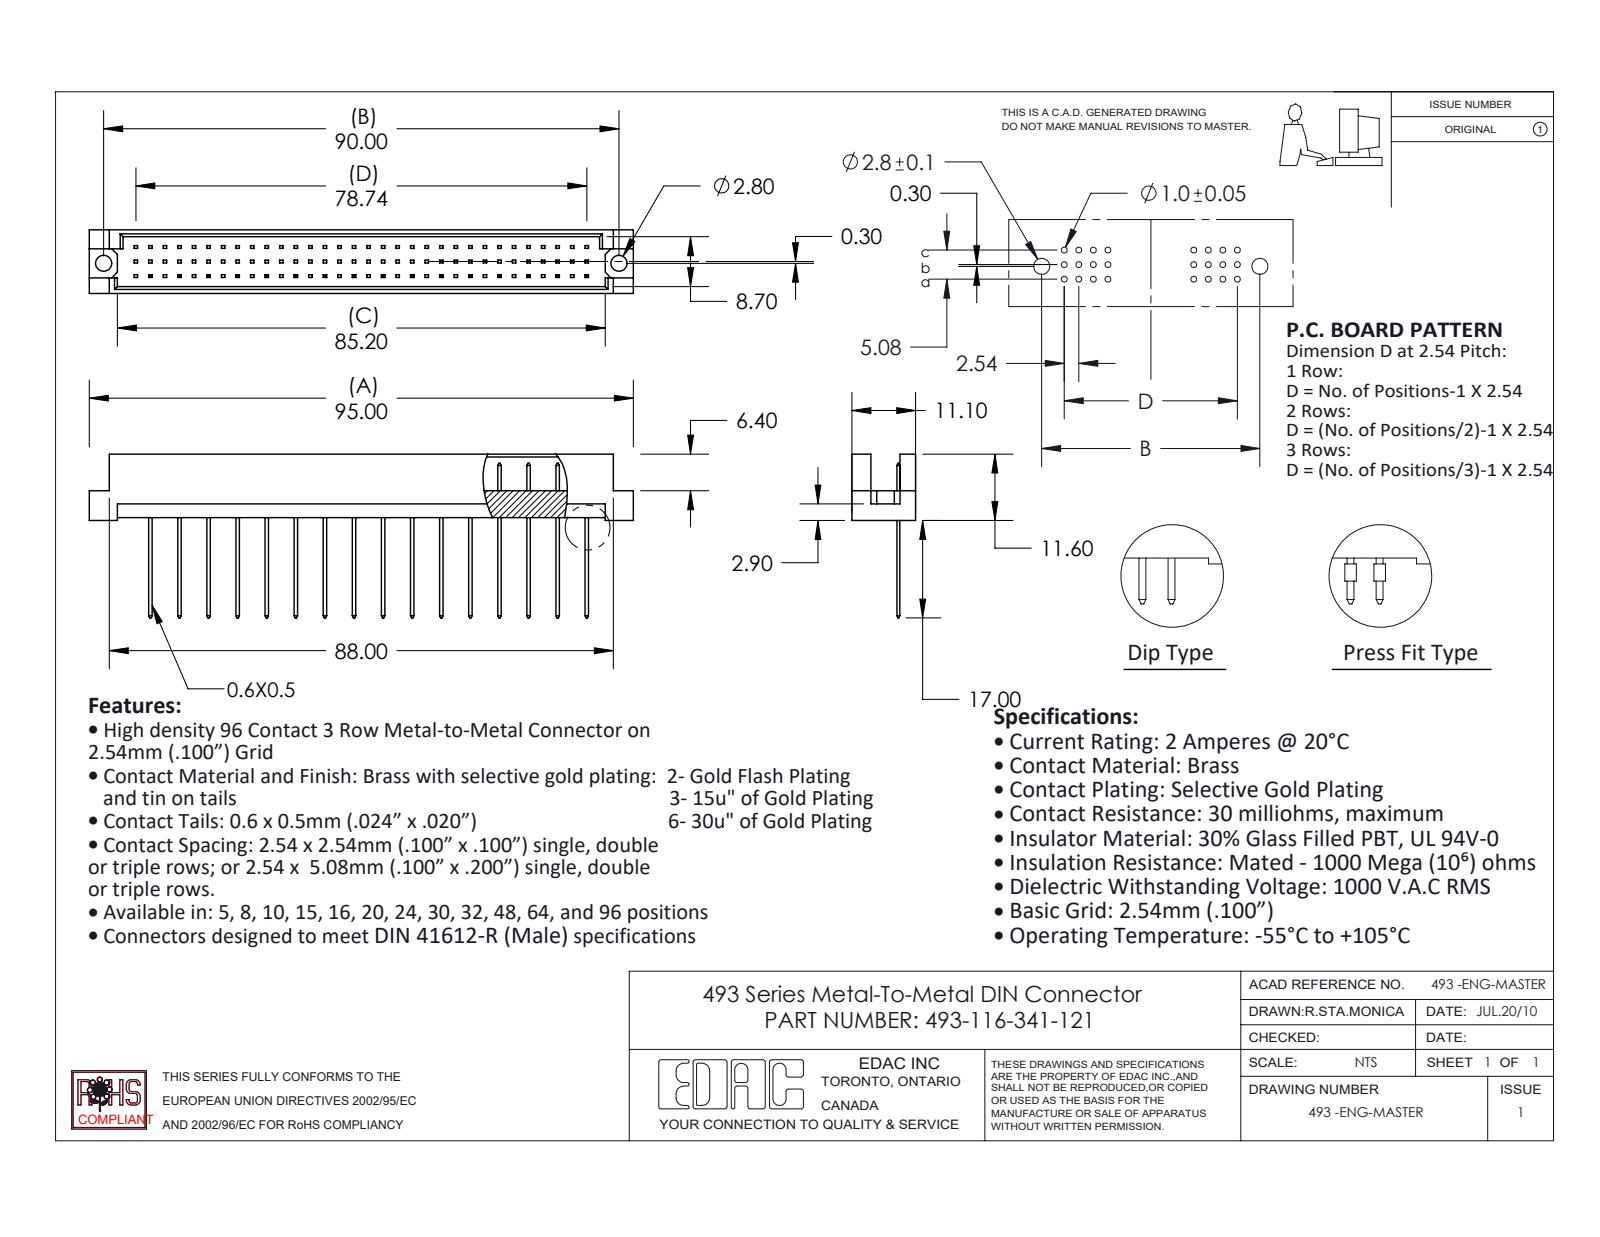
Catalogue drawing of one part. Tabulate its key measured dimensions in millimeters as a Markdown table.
| quantity | value |
| --- | --- |
| part name | 493 Part_96; 493-290_41; 493-116-341-121 |
| STEP written by | SolidWorks 2020 (CONFIG_CONTROL_DESIGN) |
| units | millimeters |
| bodies | 17 solids, 660 faces (656 planar, 4 cylindrical, 0 other) |
| overall size | 95 × 28.6 × 11.1 |
| volume | 5 787 mm³ |
| surface area | 7 419 mm² |
| round holes (diameter × count) | 2.8 × 2 |
| main face-to-face distances | 1.2, 9.9, 11.1, 8.7, 4.7, 0.5, 5.08, 3.26, 7.84, 2.06 |
| hole center spacings | 90 |
